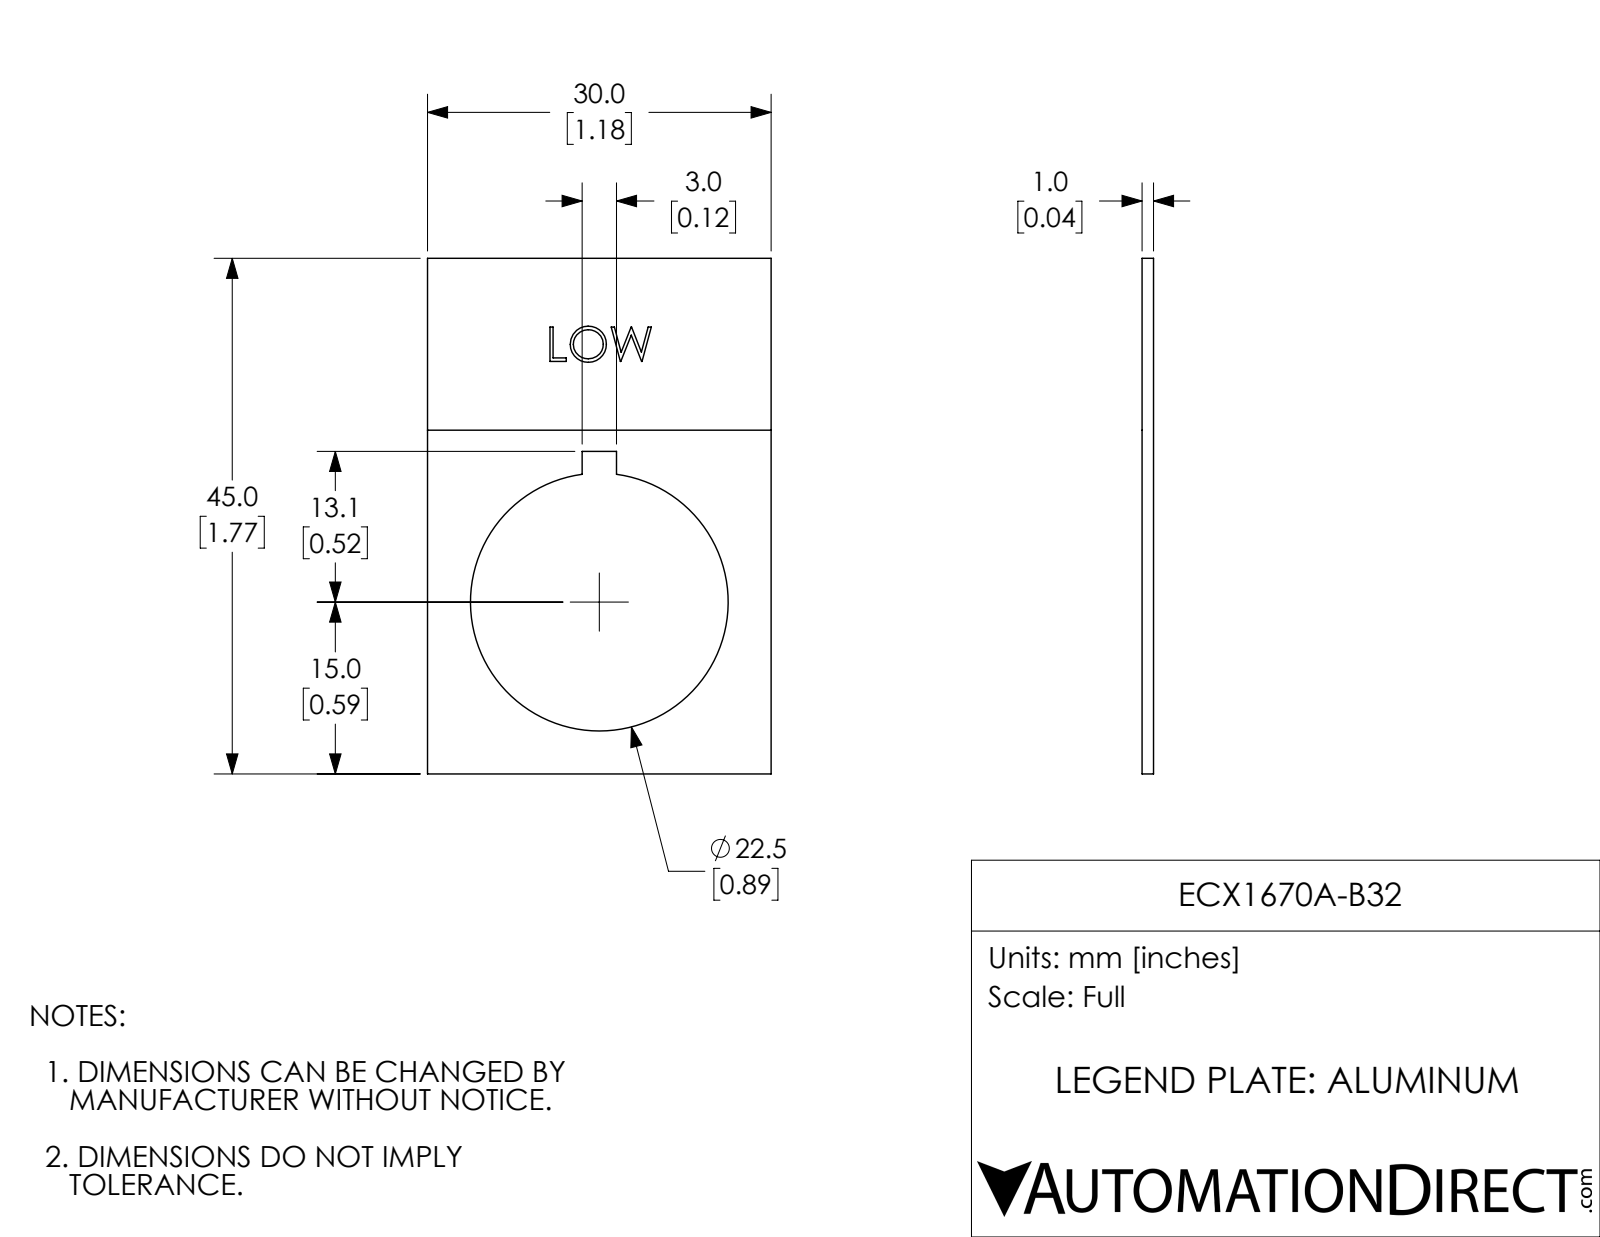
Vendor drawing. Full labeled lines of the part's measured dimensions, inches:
Part name (STEP PRODUCT): ECX1670A-B32
STEP written by: SolidWorks 2017 (AUTOMOTIVE_DESIGN)
Units: inches
Bodies: 1 solid, 44 faces (33 planar, 3 cylindrical, 8 other)
Overall size (bounding box): 1.772 × 1.181 × 0.039
Volume: 0.058 in³ · Surface area: 3.285 in²
Round holes (diameter × count): ⌀0.886 ×1
Main face-to-face distances: 0.039, 1.181, 1.772, 0.038, 0.531, 0.65, 1.108, 0.663, 0.118, 0.421
